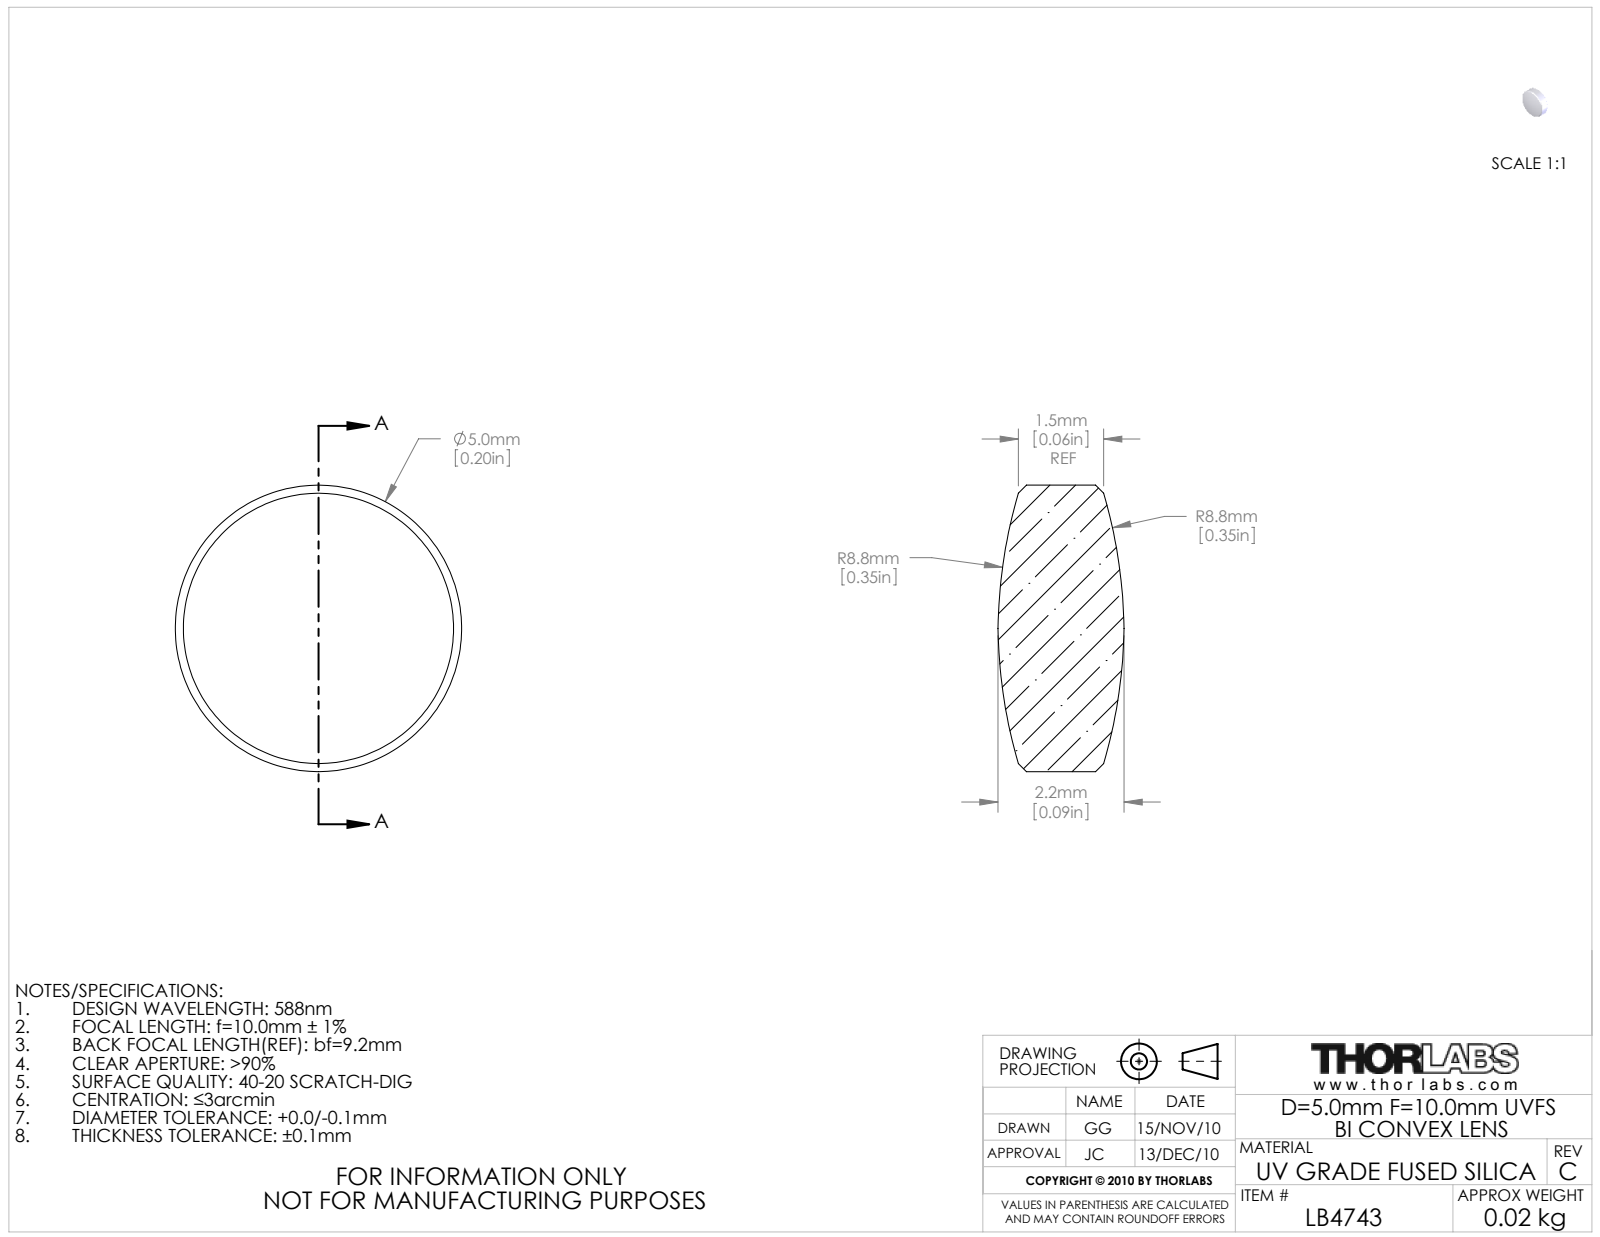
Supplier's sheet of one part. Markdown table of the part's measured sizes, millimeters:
| quantity | value |
| --- | --- |
| part name | 3388-E0W |
| STEP written by | SolidWorks 2009 (AUTOMOTIVE_DESIGN) |
| units | millimeters |
| bodies | 1 solid, 10 faces (0 planar, 2 cylindrical, 8 other) |
| overall size | 5 × 5 × 2.2 |
| volume | 35 mm³ |
| surface area | 61 mm² |
| round bosses / shafts (diameter × count) | 5 × 1 |
